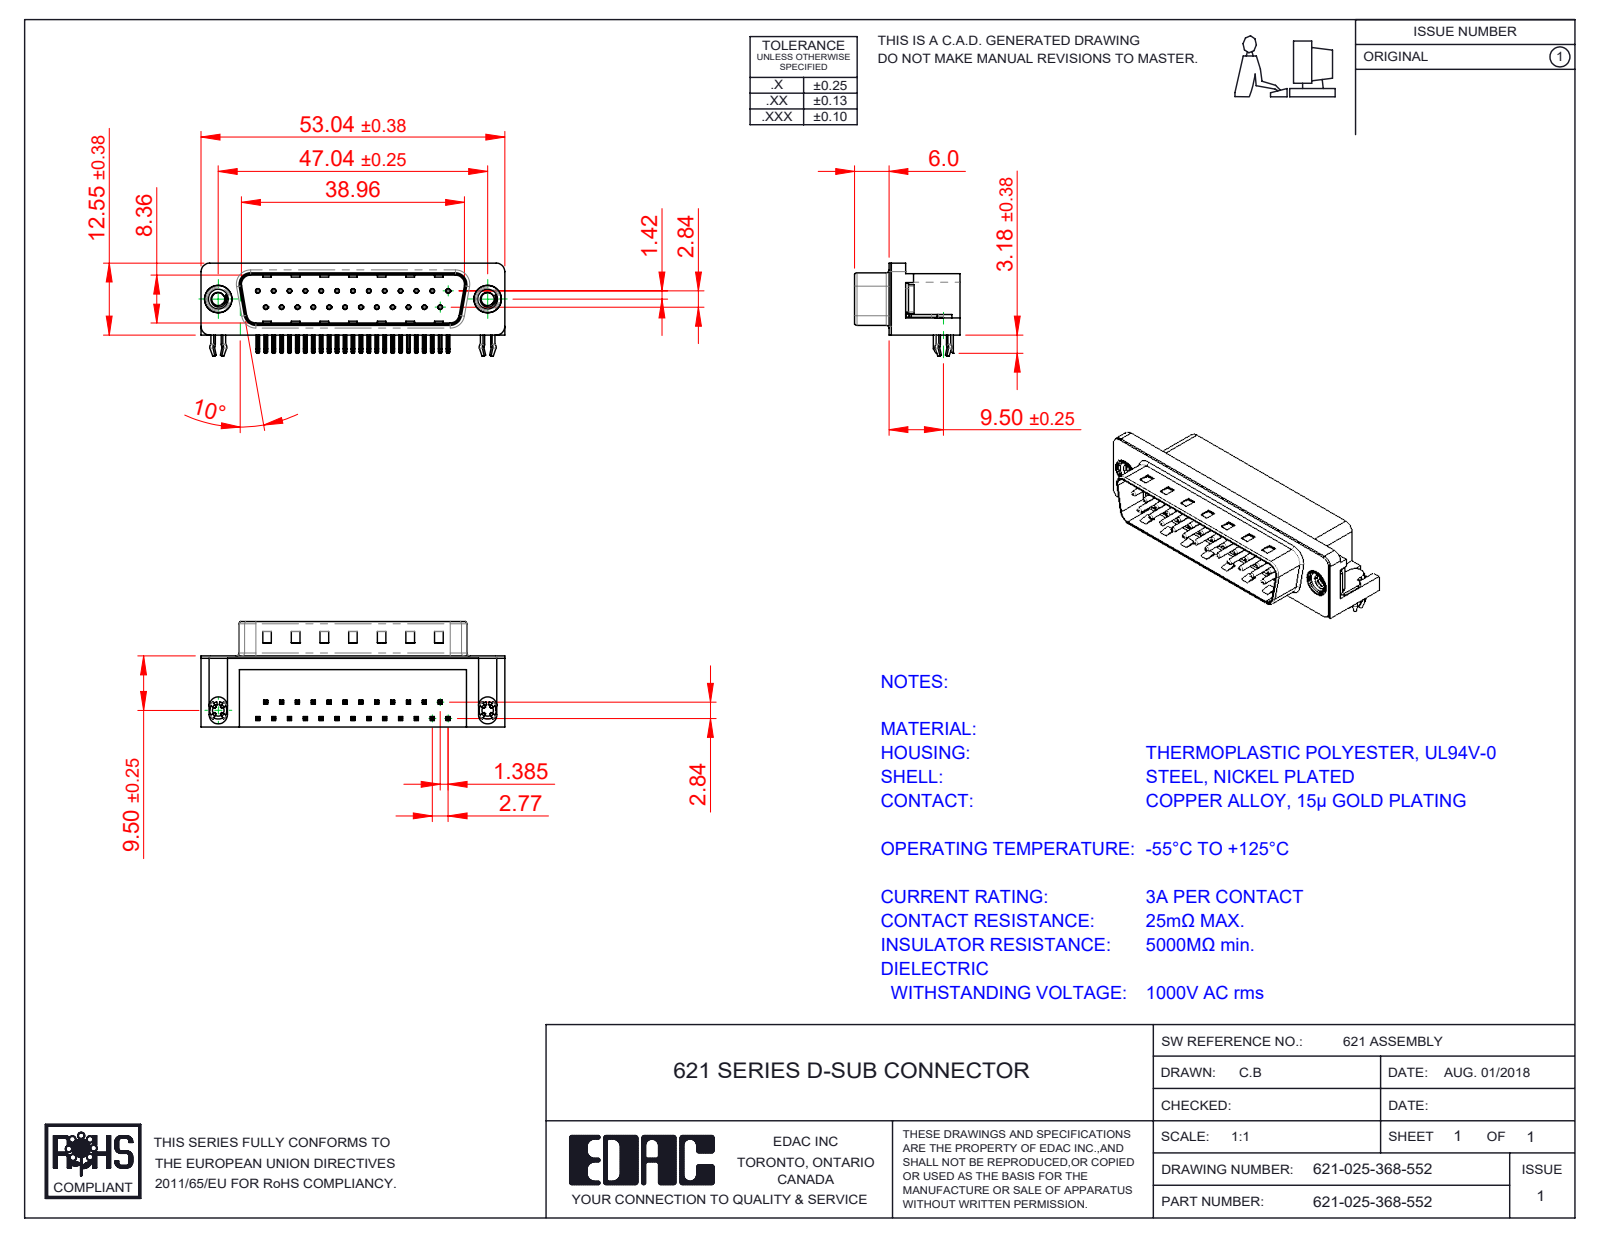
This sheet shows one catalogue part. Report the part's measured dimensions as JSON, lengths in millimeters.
{"part_name": "621-025-368-552; 621 Housing_25 Socket; 621 Contact Top; 621 Contact Bottom (+3 more)", "step_written_by": "SolidWorks 2016 (CONFIG_CONTROL_DESIGN)", "units": "millimeters", "bodies": {"solids": 31, "faces": 2293, "planar": 1405, "cylindrical": 671, "other": 217}, "overall_size": [53.04, 18.4, 15.73], "volume_mm3": 6360, "surface_area_mm2": 7762, "round_holes": [[0.35, 25], [0.8, 25], [2.26, 4], [4, 2], [4.8, 2], [5, 2]], "round_bosses_or_shafts": [[0.75, 25], [4.9, 2], [4.75, 2], [3.9, 2], [3.26, 2]], "partial_cylinders_radius": [[0.25, 108], [0.12, 50], [1, 16], [0.5, 9], [1.6, 8], [1.5, 7], [0.9, 4], [2, 4]], "face_to_face_distances": [0.4, 12, 10.35, 2.1, 8.76, 10.46, 1.7, 10.86, 12.4, 9], "hole_center_spacings": [3.16, 2.77, 5.54, 8.31, 11.08, 13.85, 16.62, 5.03]}
